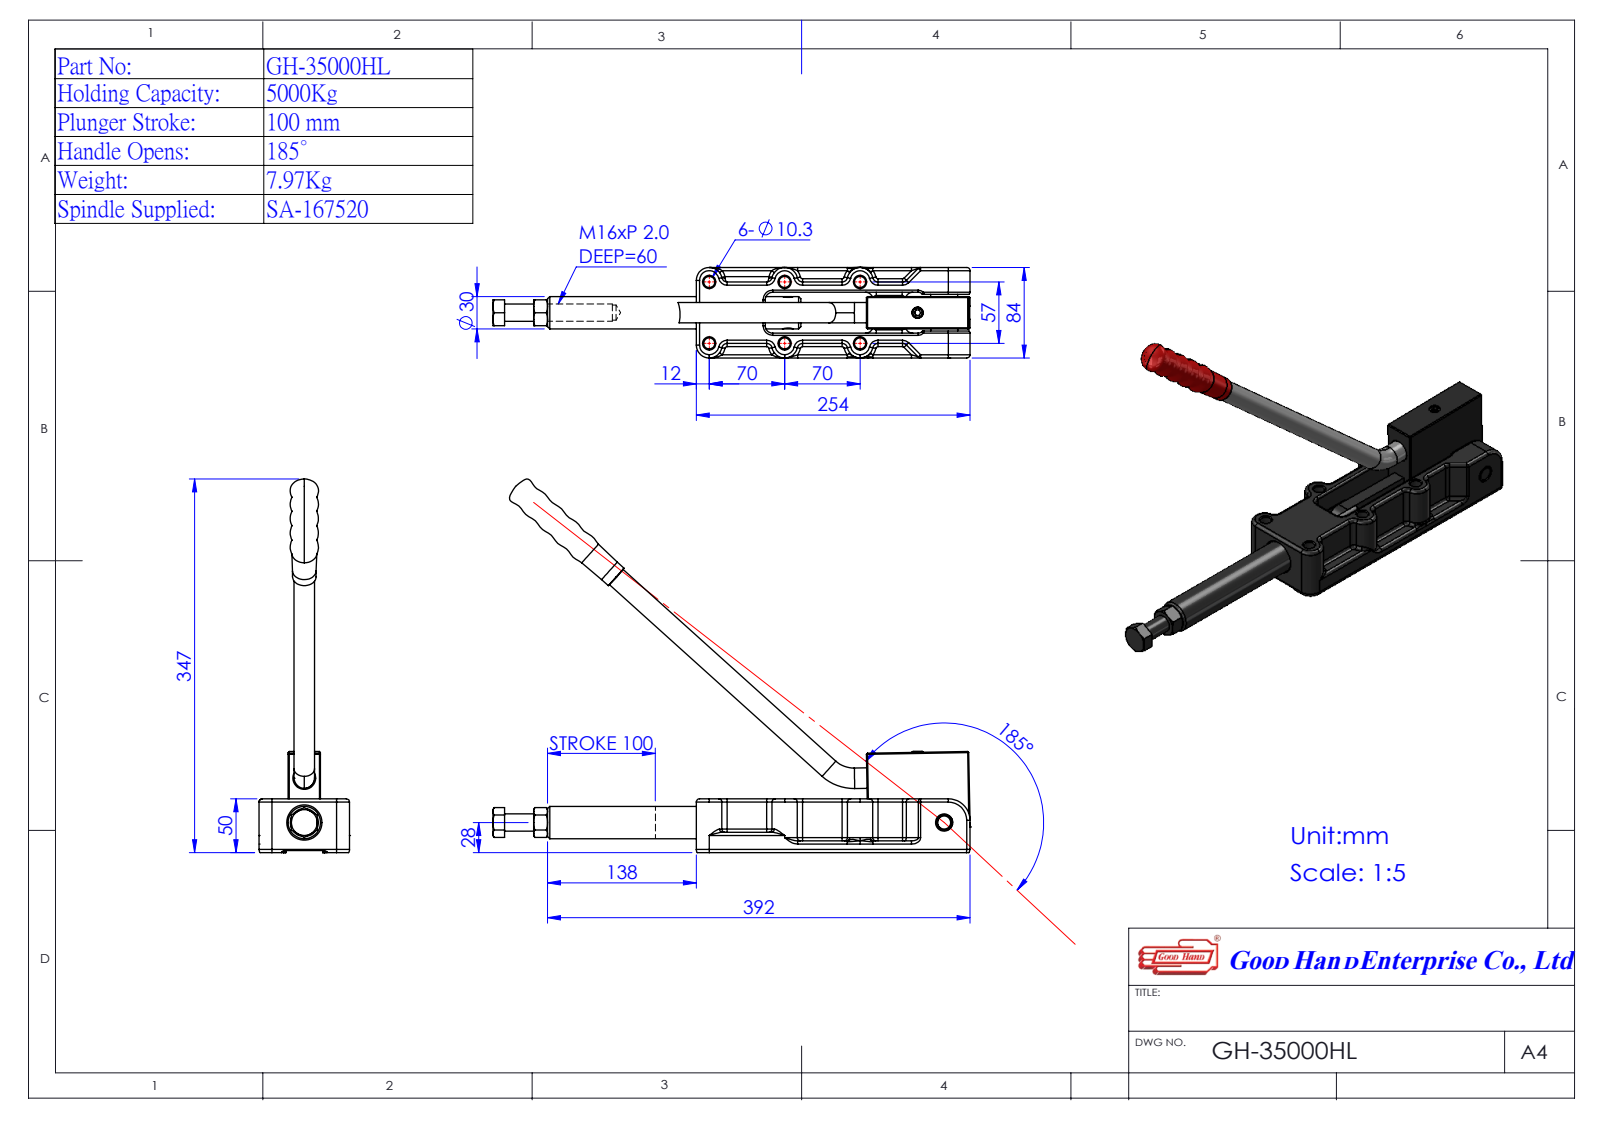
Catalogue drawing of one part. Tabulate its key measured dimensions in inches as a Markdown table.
| quantity | value |
| --- | --- |
| part name | 43500005-1^GH-35000HL(簡化)-1; Group3^GH-35000HL(簡化)-1; Group1^GH-35000HL(簡化); GH-35000HL(簡化)-1 (+2 more) |
| STEP written by | SolidWorks 2016 (AUTOMOTIVE_DESIGN) |
| units | inches |
| bodies | 5 solids, 195 faces (85 planar, 75 cylindrical, 35 other) |
| overall size | 17.864 × 13.667 × 3.307 |
| volume | 64.07 in³ |
| surface area | 312.4 in² |
| round holes (diameter × count) | 0.406 × 6, 0.315 × 2, 0.335 × 1, 0.433 × 1, 0.551 × 1, 1.181 × 1 |
| round bosses / shafts (diameter × count) | 0.748 × 2, 0.945 × 1, 0.858 × 1, 0.63 × 1, 0.315 × 1 |
| partial cylindrical surfaces (radius × count) | 0.197 × 11, 0.472 × 6, 0.276 × 2, 0.551 × 2, 0.787 × 1 |
| main face-to-face distances | 0.163, 1.333, 1.496, 0.906, 1.069, 2.238, 2.402, 1.969, 1.169, 0.531 |
| hole center spacings | 2.756, 3.554, 2.244, 5.512, 5.951, 2.087, 3.622, 5.708 |
